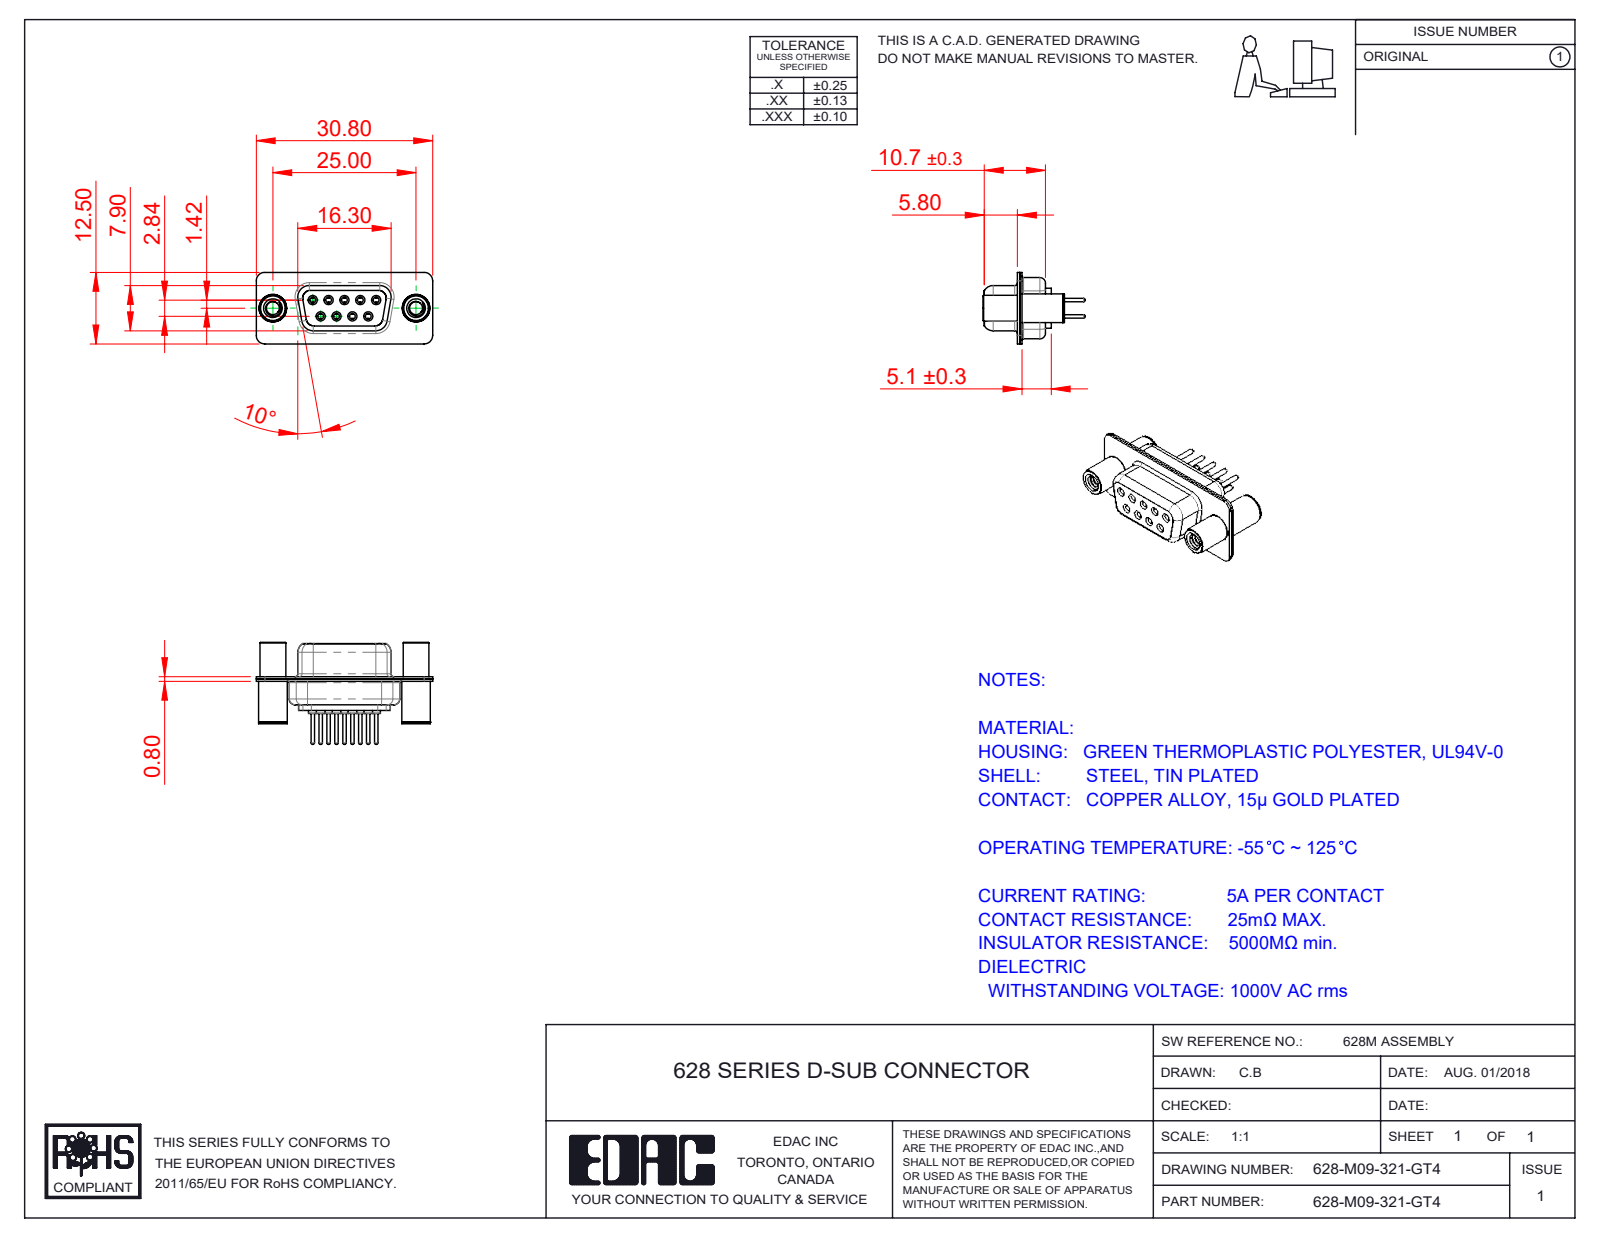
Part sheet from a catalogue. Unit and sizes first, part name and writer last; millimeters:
Units: millimetres
Overall size (bounding box): 30.8 × 17.8 × 12.5
Round holes (diameter × count): ⌀1 ×9, ⌀1.1 ×9, ⌀1.7 ×9, ⌀1.8 ×9, ⌀2 ×9, ⌀2.26 ×2, ⌀3.26 ×2, ⌀4 ×2, ⌀4.8 ×2
Round bosses / shafts (diameter × count): ⌀2.2 ×9, ⌀1.6 ×9, ⌀1.5 ×9, ⌀0.6 ×9, ⌀5 ×2, ⌀4.9 ×2, ⌀4.5 ×2
Partial cylindrical surfaces — rounded edges, fillets, slot ends (radius × count): R1.5 ×16, R2 ×12, R1.35 ×8, R1.6 ×8, R0.25 ×4, R0.5 ×4, R0.6 ×4, R0.65 ×4
Main face-to-face distances: 0.4, 1.4, 0.45, 8.45, 0.8, 1.8, 8.9, 1, 6.2, 7.05
Hole centre spacings: 3.16, 2.77, 5.54, 5.03, 5.04, 8.31, 7.1, 7.48
Volume: 1 989 mm³ · Surface area: 4 952 mm²
Bodies: 14 solids, 860 faces (208 planar, 360 cylindrical, 292 other)
Part name (STEP PRODUCT): 628M Housing_09 Contacts; 628-M09-321-GT4; 628M Contact Row 2_21; 628M Contact Row 1_21 (+3 more)
STEP written by: SolidWorks 2020 (CONFIG_CONTROL_DESIGN)
